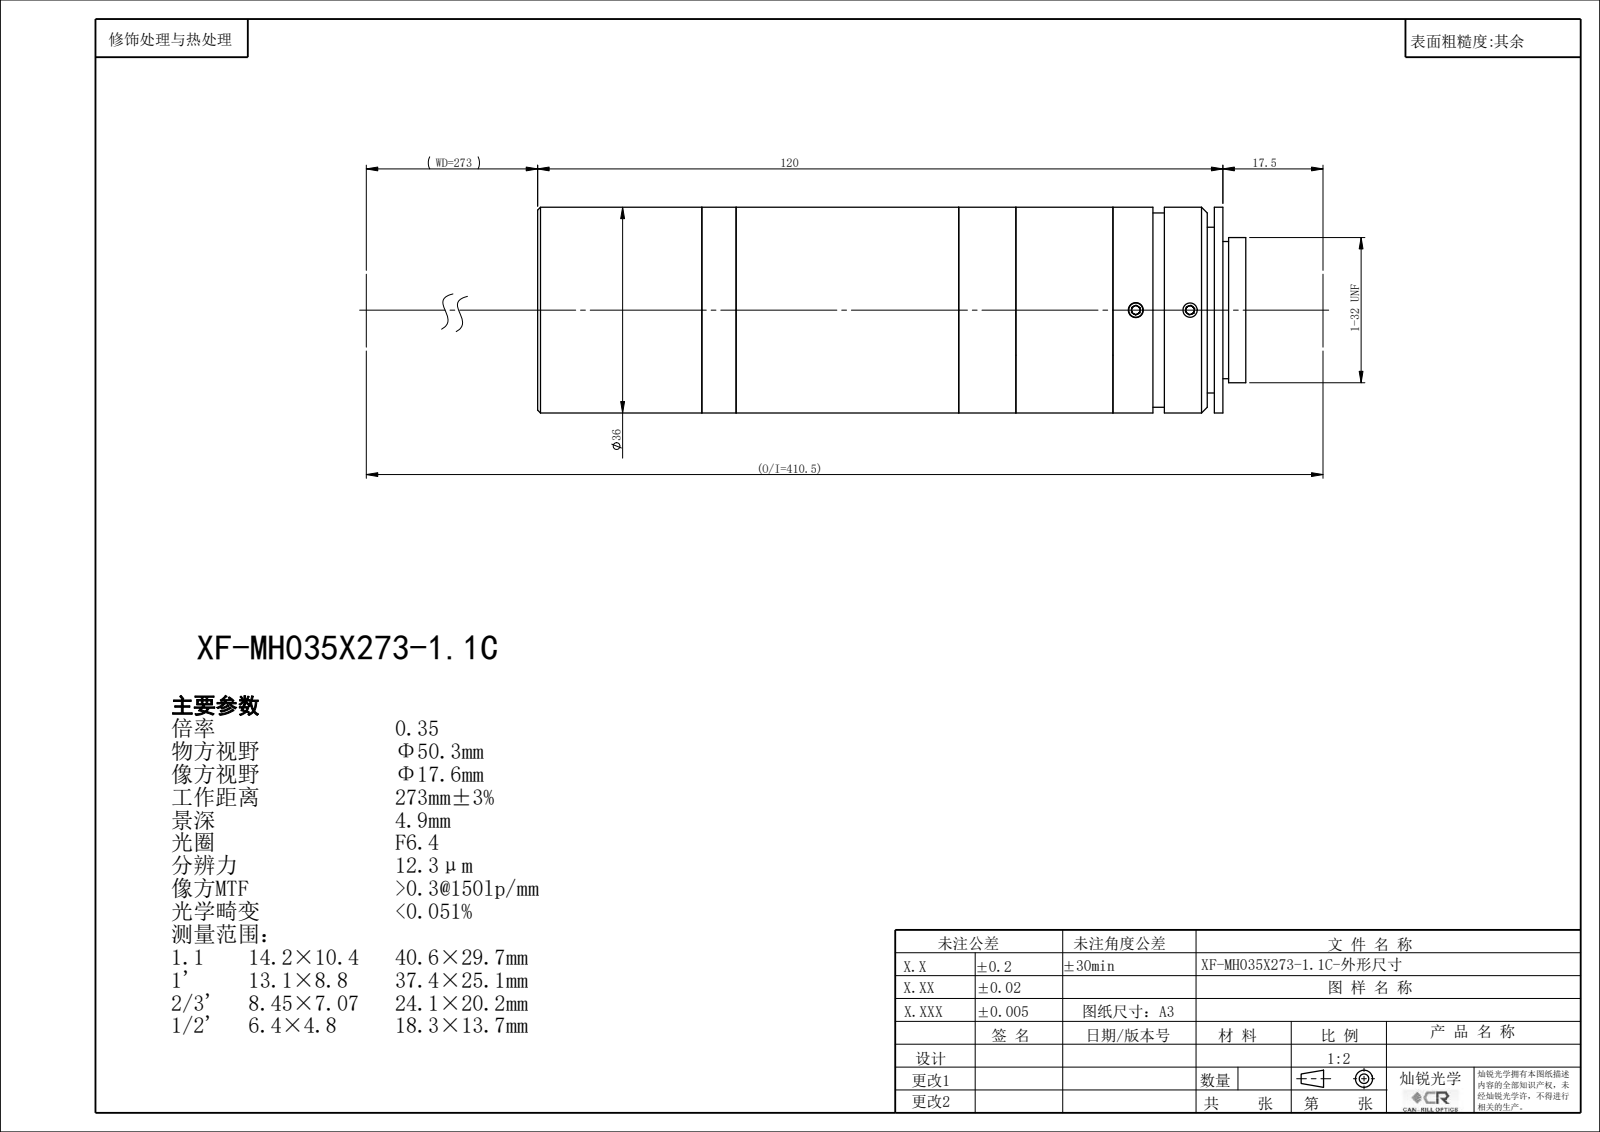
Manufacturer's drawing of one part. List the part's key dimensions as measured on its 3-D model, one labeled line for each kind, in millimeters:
Part name (STEP PRODUCT): XF-MH035X273-1.1C
STEP written by: SolidWorks 2022 (CONFIG_CONTROL_DESIGN)
Units: millimetres
Bodies: 0 solids, 134 faces (70 planar, 42 cylindrical, 22 other)
Overall size (bounding box): 123.96 × 36 × 36
Round holes (diameter × count): ⌀2.5 ×3, ⌀22.4 ×1, ⌀24 ×1, ⌀26 ×1, ⌀26.4 ×1, ⌀29.4 ×1, ⌀33.4 ×1, ⌀34.5 ×1
Round bosses / shafts (diameter × count): ⌀36 ×1, ⌀34 ×1, ⌀25.4 ×1
Main face-to-face distances: 19.24, 1.5, 17.74, 34.74, 17, 36.24, 10, 27, 44.74, 46.24
